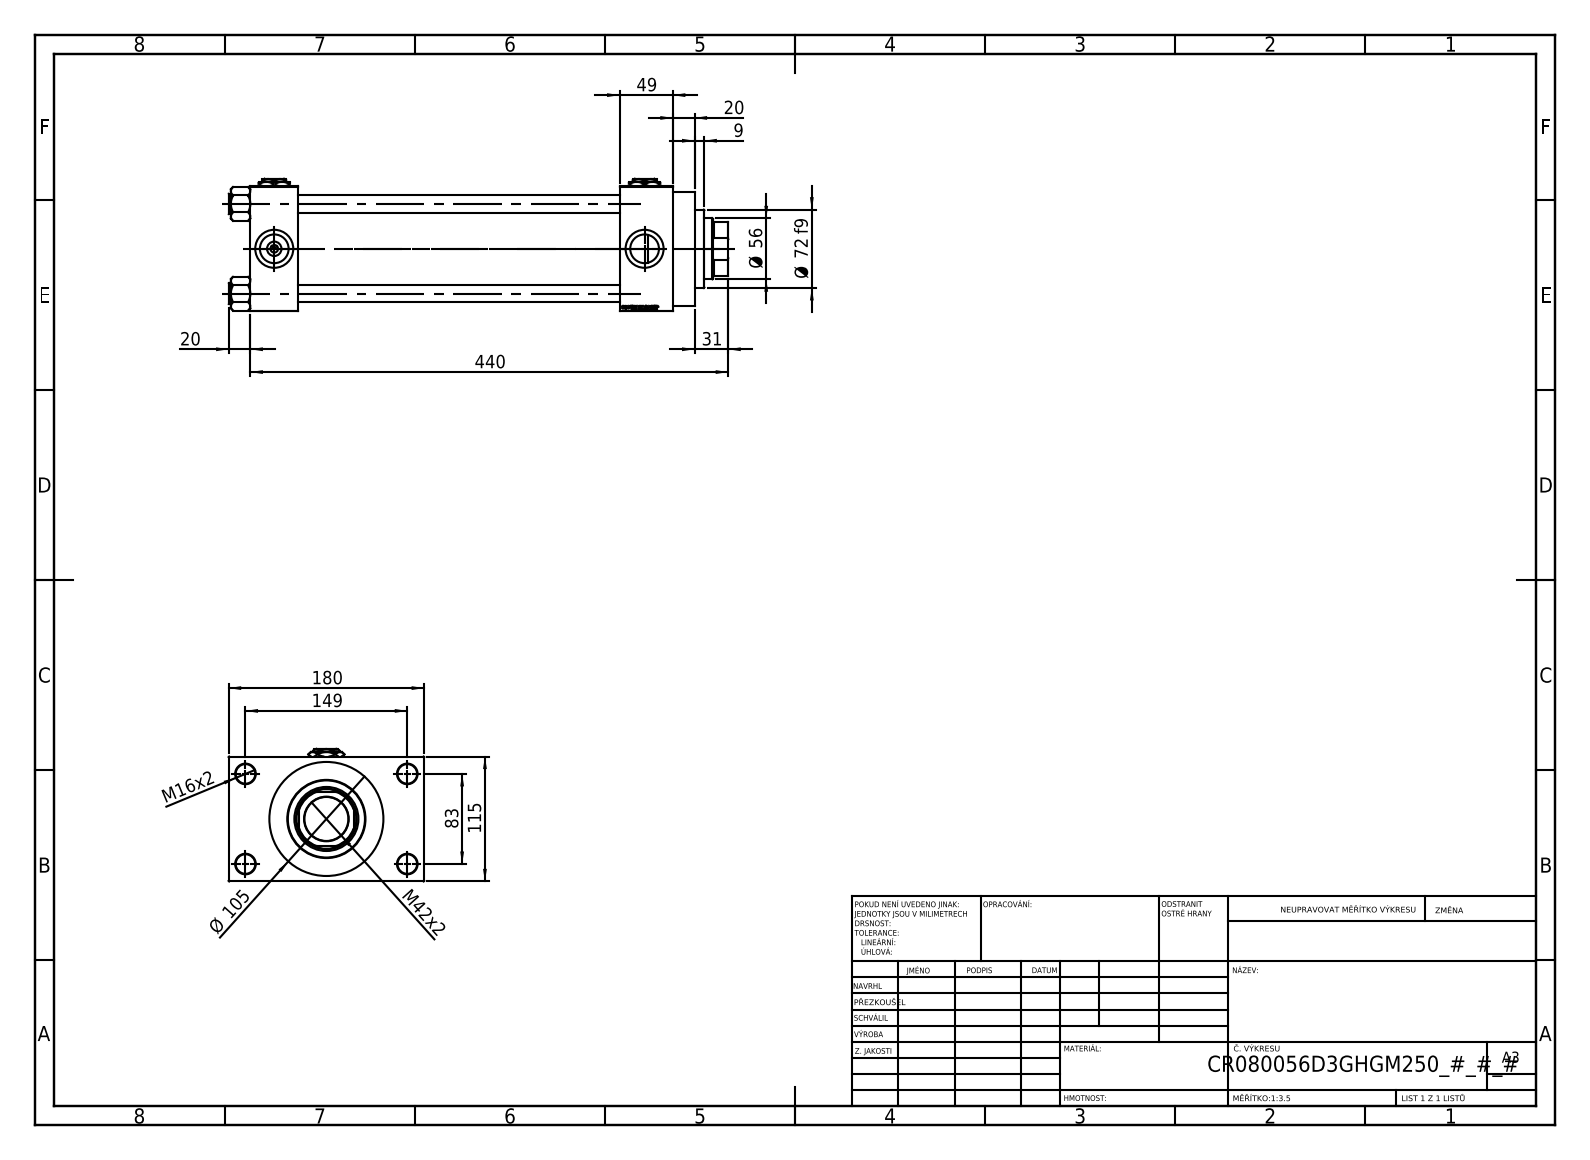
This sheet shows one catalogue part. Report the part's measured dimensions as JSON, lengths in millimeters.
{"part_name": "V215CR_D_TYCINKA; Zatka_pro_OIL_PORT; V215CR_D_Body; V215_VC_A (+2 more)", "step_written_by": "SolidWorks 2019 (CONFIG_CONTROL_DESIGN)", "units": "millimeters", "bodies": {"solids": 13, "faces": 1249, "planar": 592, "cylindrical": 97, "other": 560}, "overall_size": [460, 180, 122], "volume_mm3": 3019000, "surface_area_mm2": 524101, "round_holes": [[16, 4], [18, 4], [26.44, 4], [35, 4], [7, 3], [40.5, 1], [56, 1], [59, 1], [61, 1], [72, 1], [80, 1]], "round_bosses_or_shafts": [[19, 4], [105, 1], [86, 1]], "partial_cylinders_radius": [[27, 1]], "face_to_face_distances": [115, 296, 44, 340, 389, 345, 49, 32.5, 147.5, 20], "hole_center_spacings": [33.15, 58.48, 82.7, 85.28, 89.24, 115.85, 142.43, 83]}
